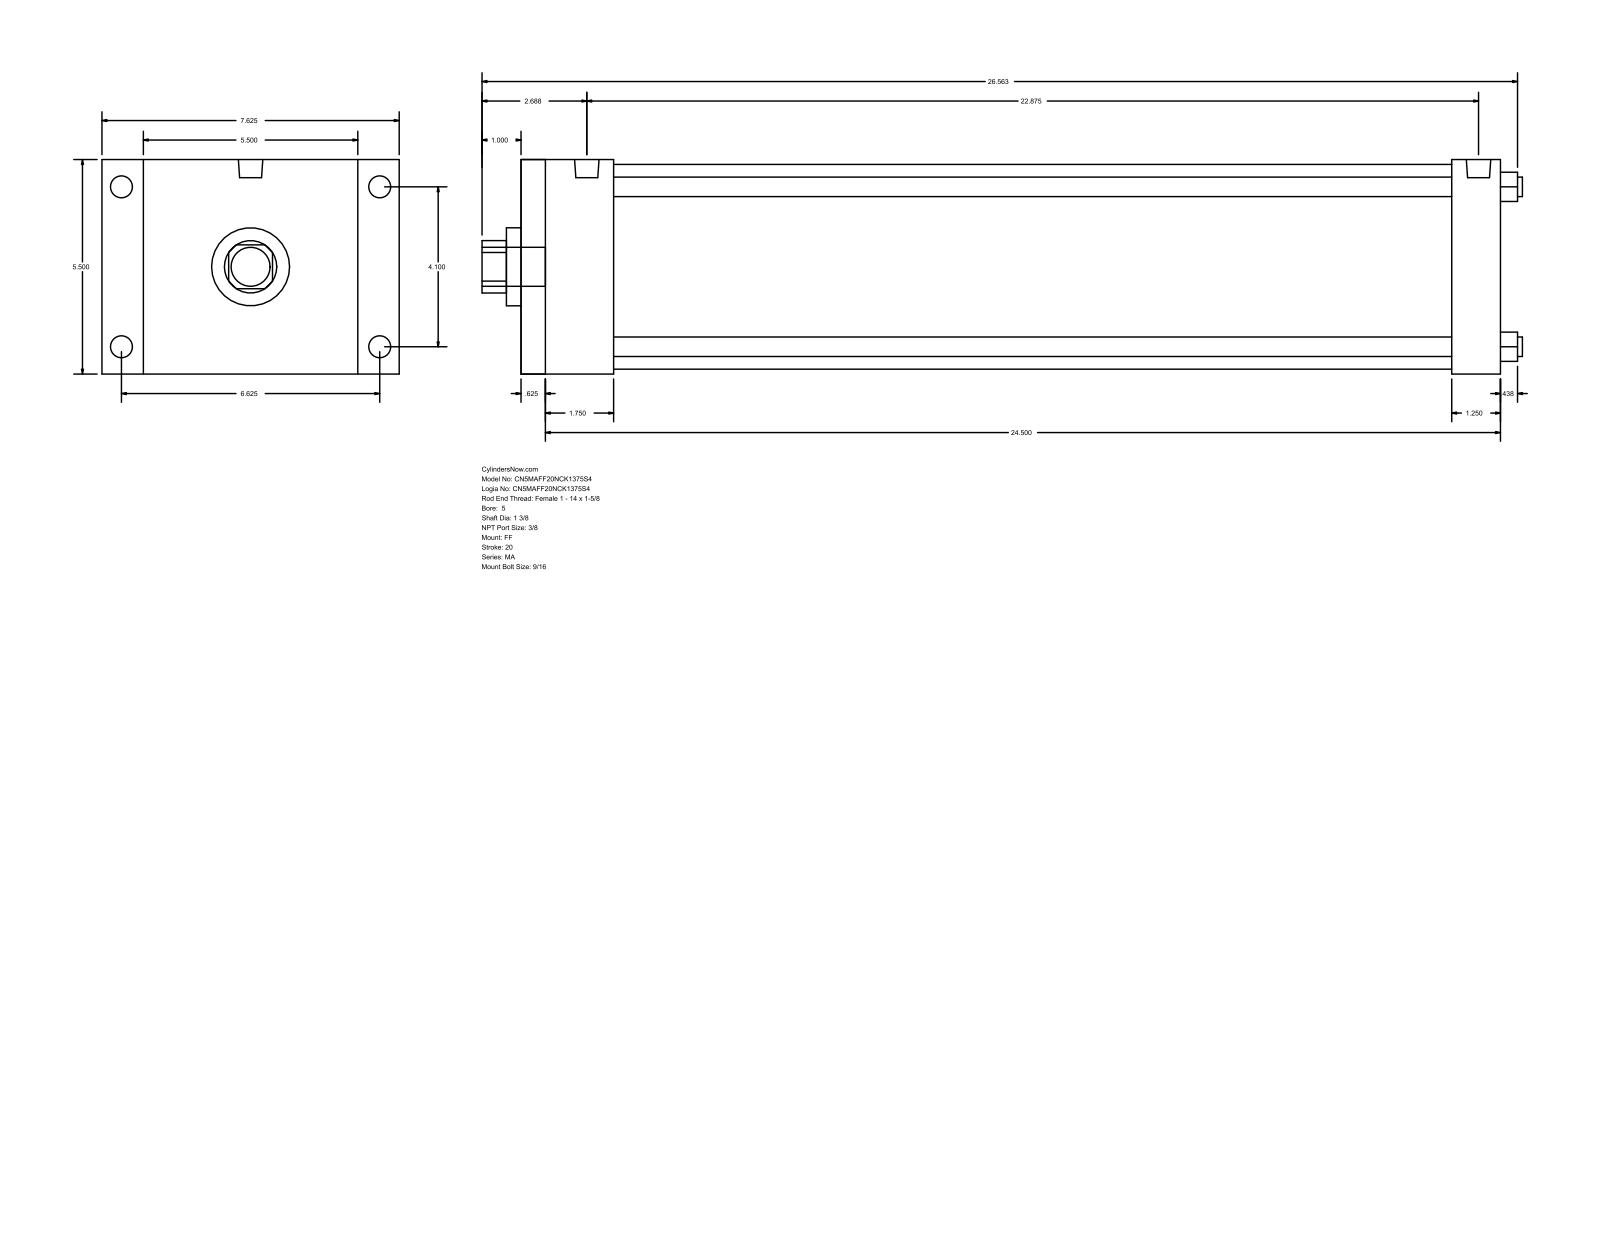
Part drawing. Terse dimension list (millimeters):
name: MA_FF__0500_1.375
written by: GSSL Pune (CONFIG_CONTROL_DESIGN)
unit: mm
bodies: 0 solids, 92 faces (64 planar, 28 cylindrical, 0 other)
size: 677.86 × 193.68 × 139.7
holes: 4× ⌀12.7, 1× ⌀34.92, 1× ⌀50.8, 1× ⌀133.35
bosses: 4× ⌀14.29, 4× ⌀11.11, 2× ⌀15.93, 1× ⌀25.4
rounds: 1× R17.06
face distances: 139.7, 638.18, 15.87, 622.31, 606.43, 590.56, 31.75, 60.32, 44.45, 546.11
hole spacings: 73.64, 104.14, 147.28
